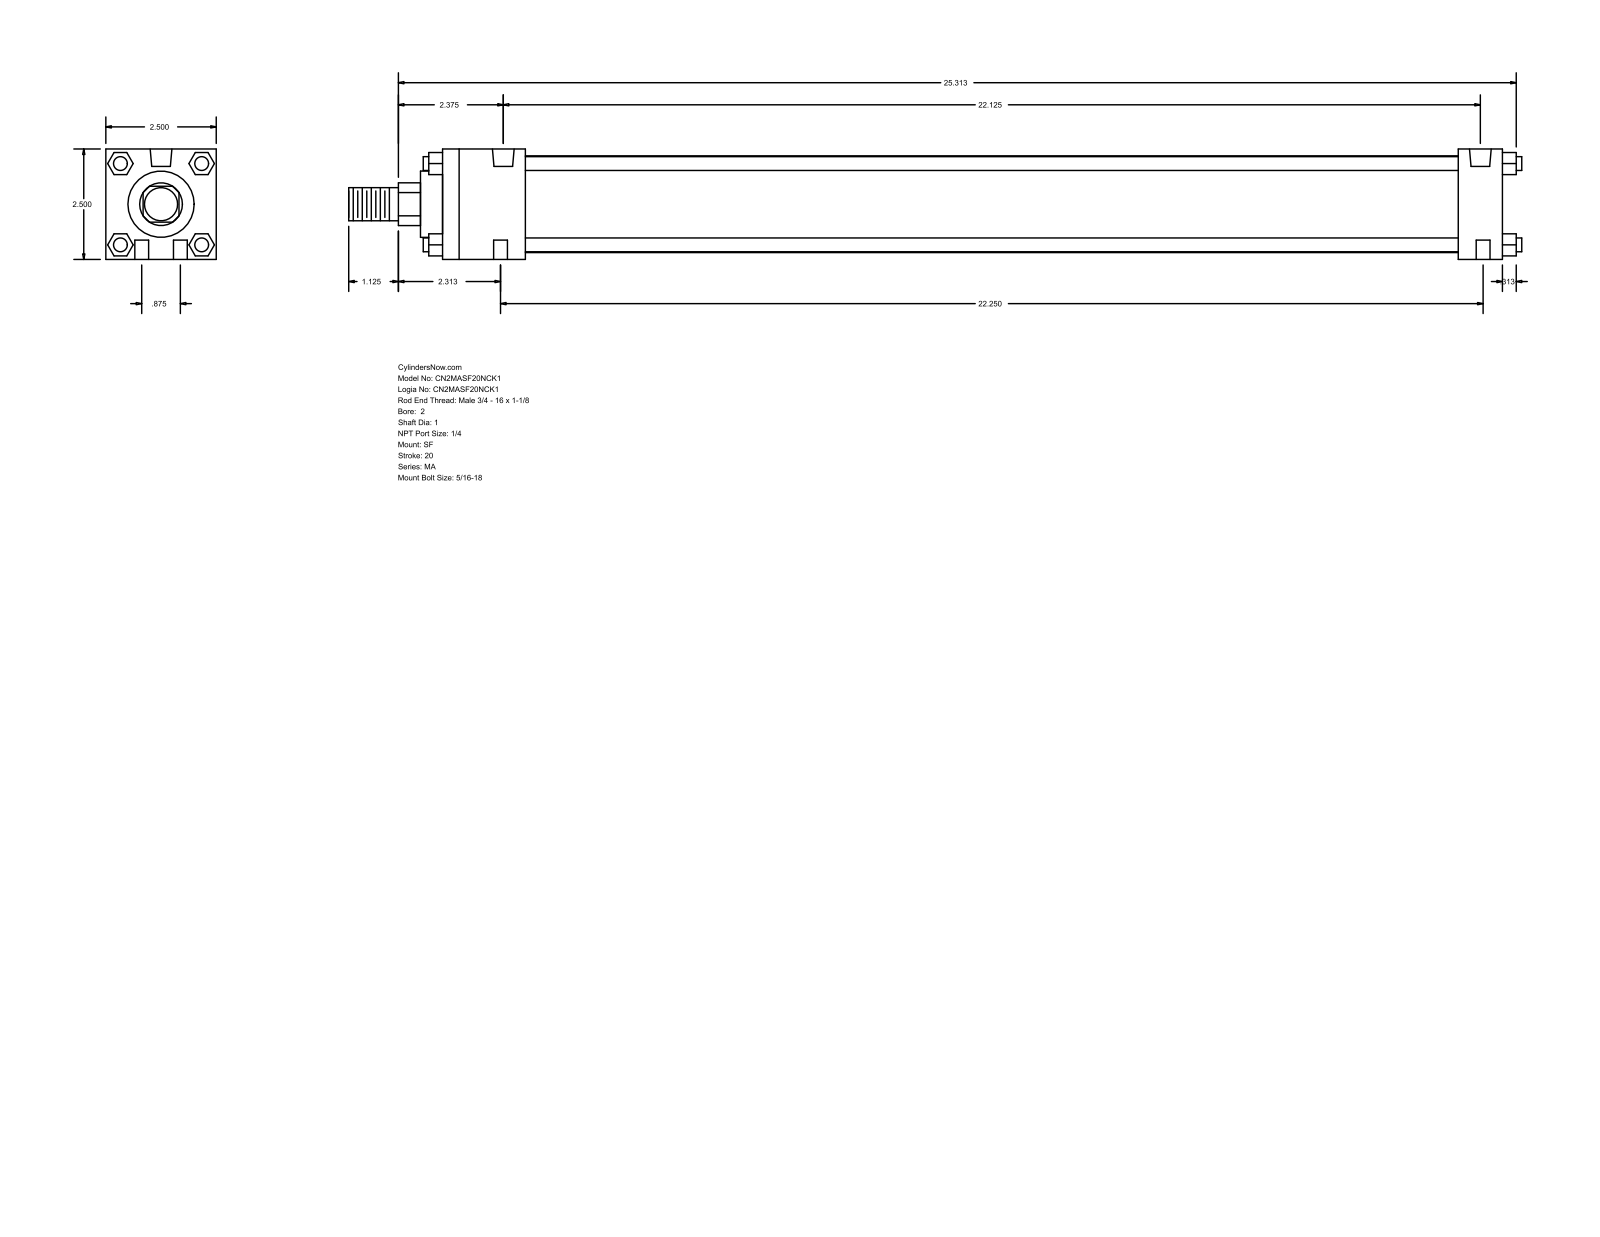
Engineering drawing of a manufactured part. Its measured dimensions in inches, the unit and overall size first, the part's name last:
Units: inches
Overall size (bounding box): 26.563 × 2.5 × 2.5
Round holes (diameter × count): ⌀0.313 ×6, ⌀0.492 ×2
Round bosses / shafts (diameter × count): ⌀0.313 ×4, ⌀2.19 ×1, ⌀1.5 ×1, ⌀1 ×1, ⌀0.75 ×1
Partial cylindrical surfaces — rounded edges, fillets, slot ends (radius × count): R0.484 ×1
Main face-to-face distances: 2.5, 24, 0.5, 1, 23, 1.875, 21.125, 22.125, 0.92, 1.593
Hole centre spacings: 0.442, 22.192, 0.875, 22.125, 22.25, 22.267
Bodies: 0 solids, 124 faces (94 planar, 30 cylindrical, 0 other)
Part name (STEP PRODUCT): MA_SF__0200_1
STEP written by: GSSL Pune (CONFIG_CONTROL_DESIGN)
